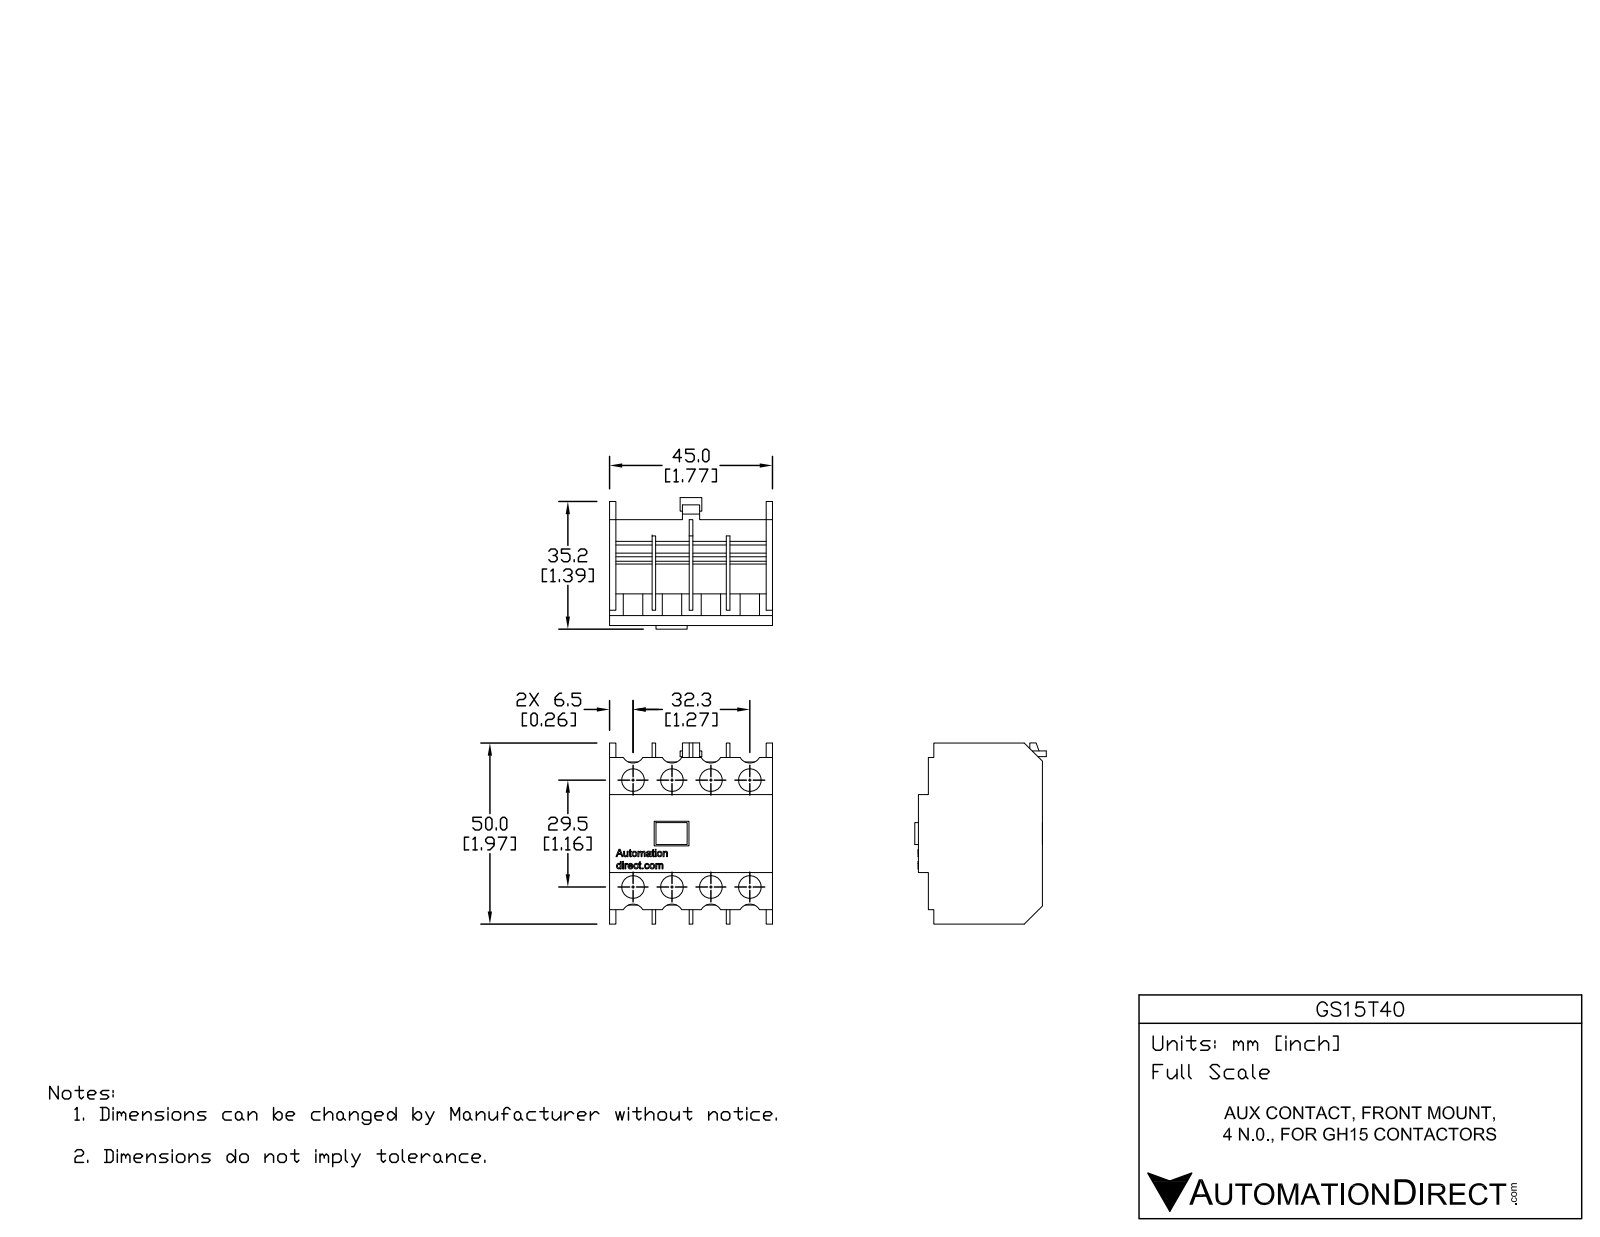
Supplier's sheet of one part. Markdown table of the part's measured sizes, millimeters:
| quantity | value |
| --- | --- |
| part name | GH15T40 |
| STEP written by | SolidWorks 2009 (CONFIG_CONTROL_DESIGN) |
| units | millimeters |
| bodies | 1 solid, 509 faces (359 planar, 24 cylindrical, 126 other) |
| overall size | 50.03 × 45 × 36.32 |
| volume | 38 863 mm³ |
| surface area | 16 844 mm² |
| round holes (diameter × count) | 6.25 × 8 |
| partial cylindrical surfaces (radius × count) | 3.12 × 8 |
| main face-to-face distances | 10.25, 20.5, 45, 1.75, 43.25, 1, 6, 22, 14.25, 12.75 |
| hole center spacings | 10.75, 31.4, 21.5, 29.5, 36.5, 32.25, 43.71 |
